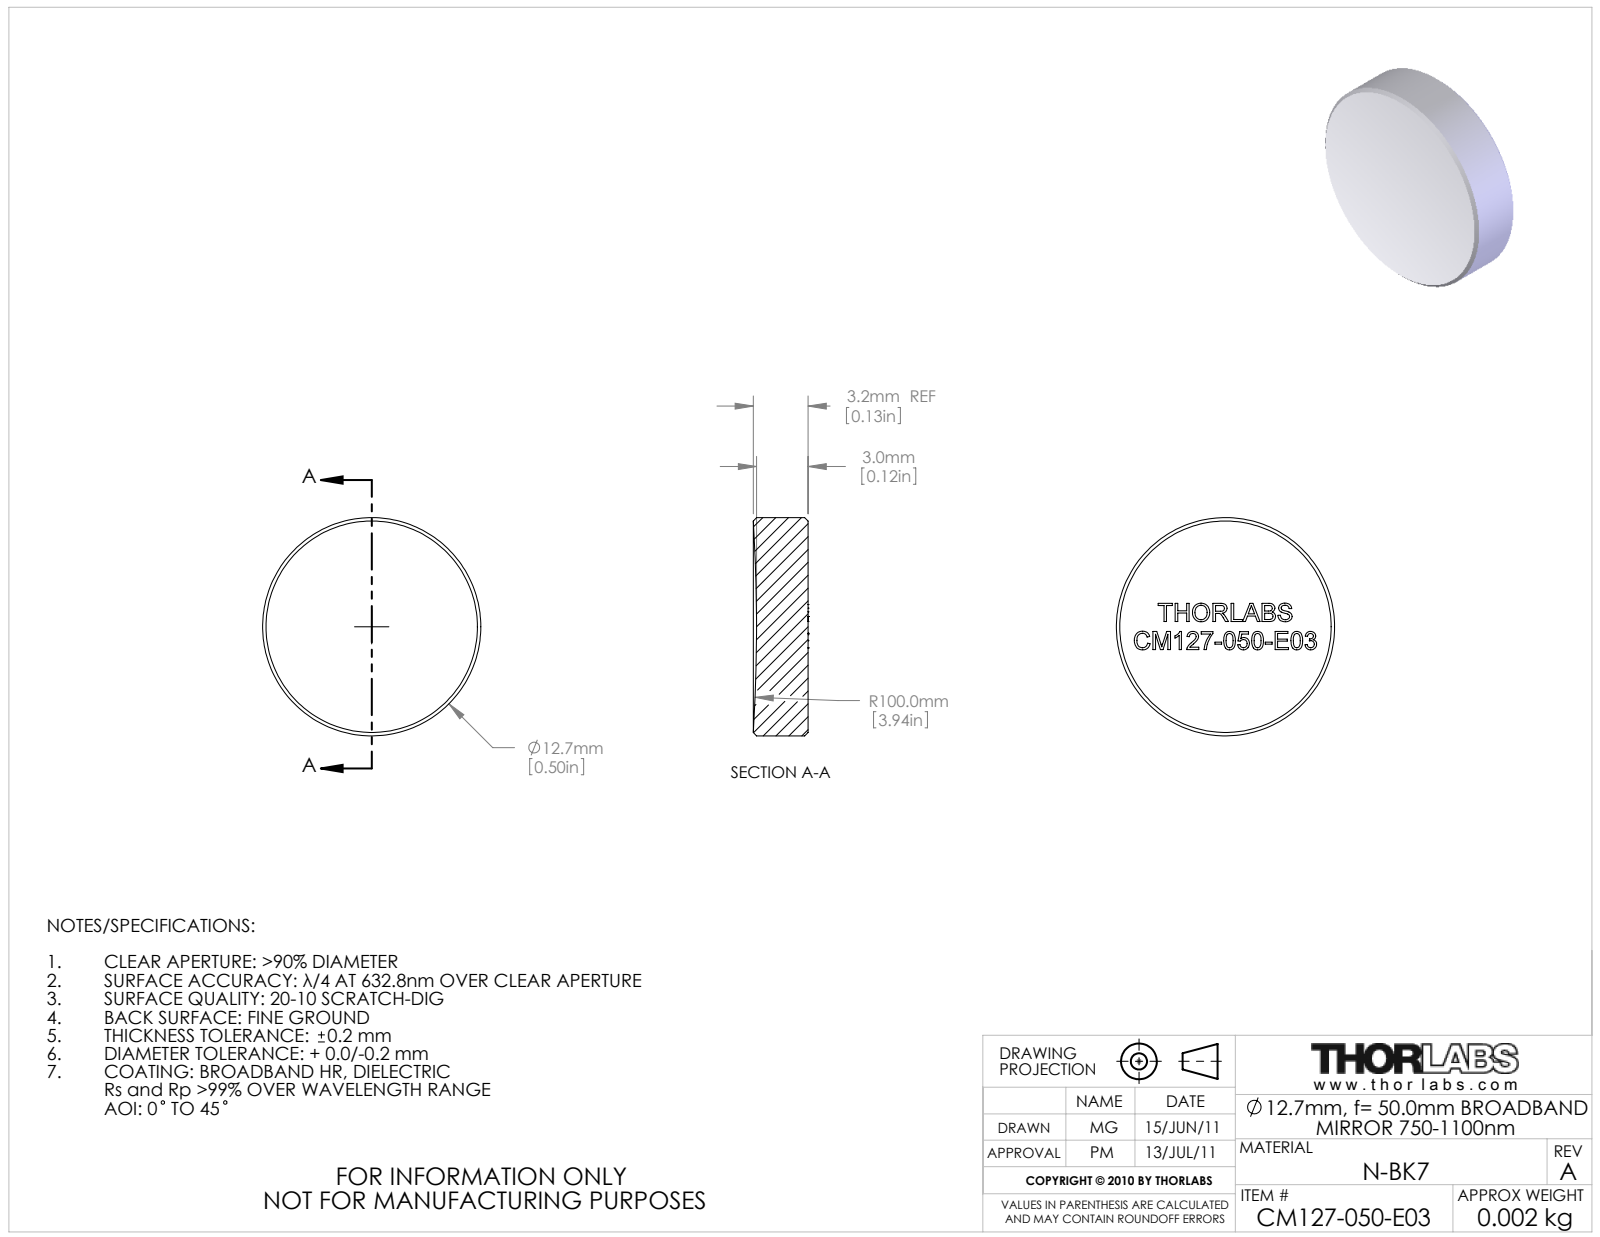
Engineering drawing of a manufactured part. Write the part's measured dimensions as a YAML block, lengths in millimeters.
part_name: "22640-E0W"
step_written_by: "SolidWorks 2011 (AUTOMOTIVE_DESIGN)"
units: millimeters
bodies: {solids: 0, faces: 41, planar: 31, cylindrical: 2, other: 8}
overall_size: [12.7, 12.7, 3.19]
round_bosses_or_shafts:
  - {diameter: 12.7, count: 1}
